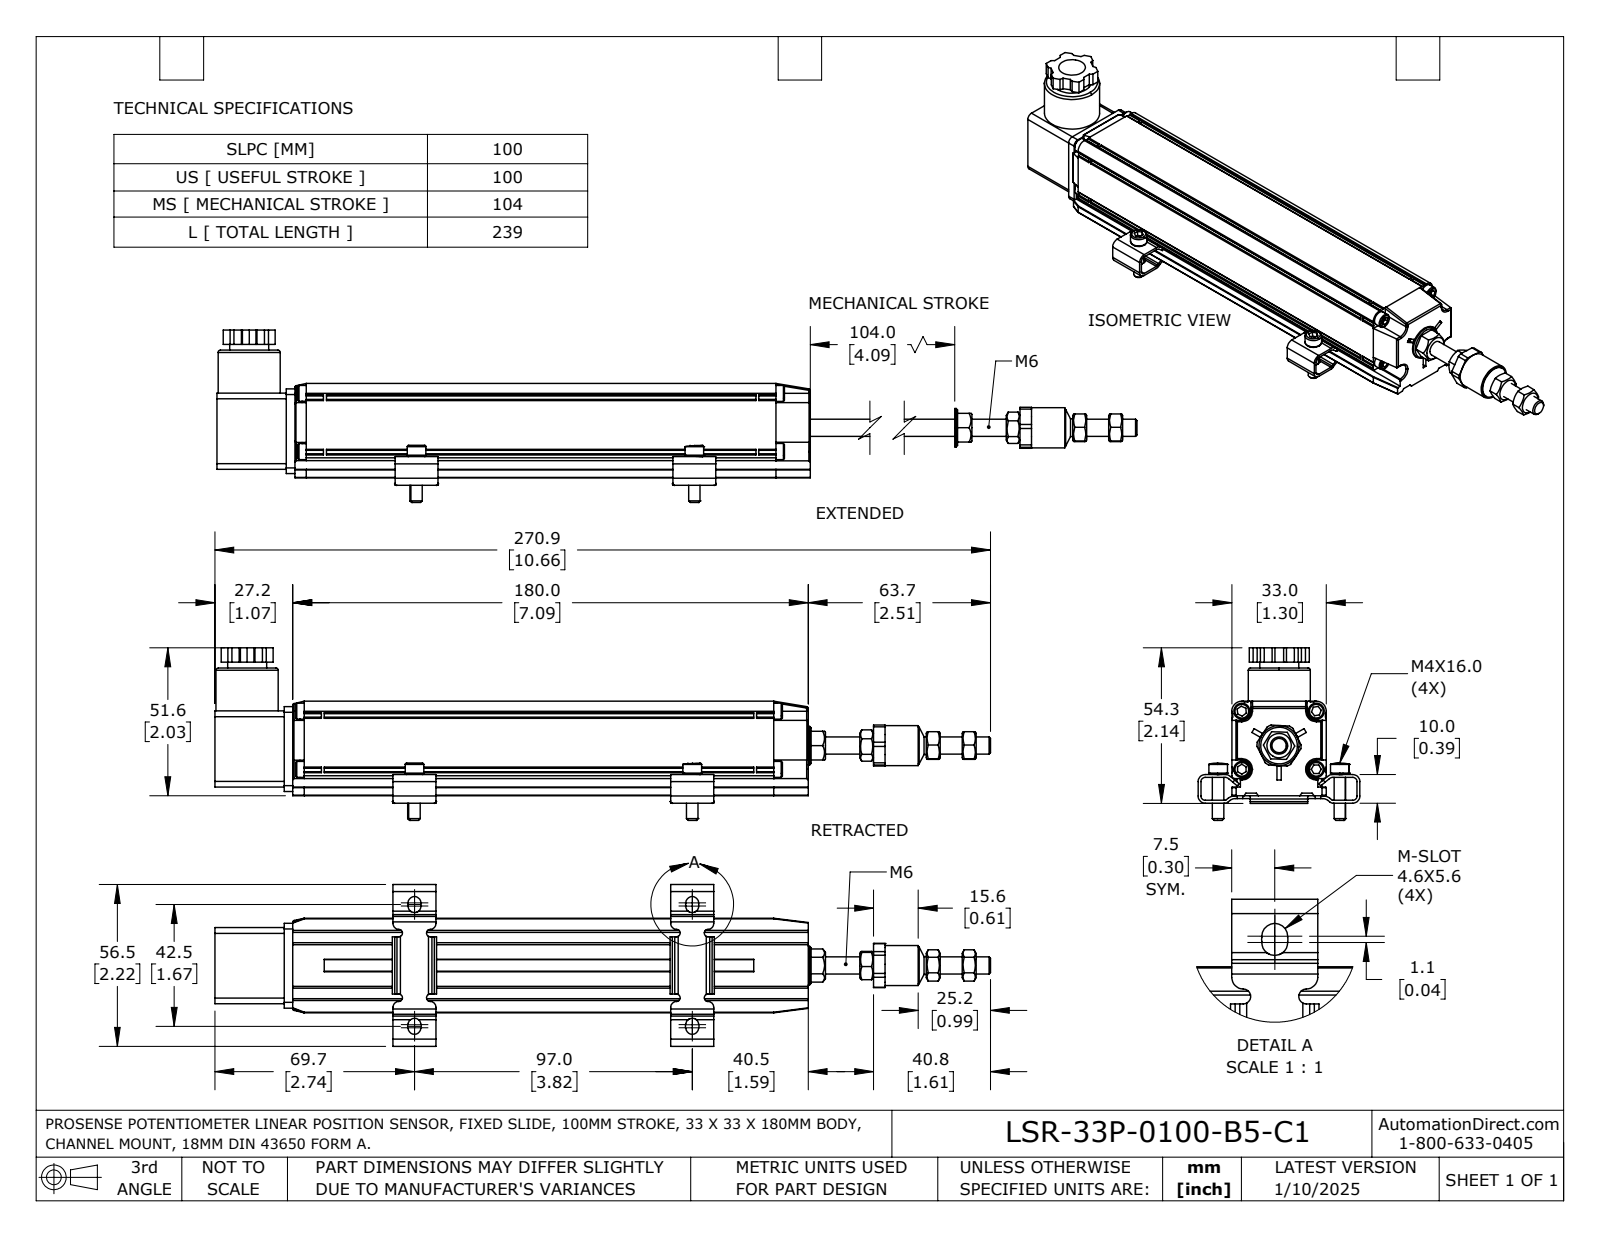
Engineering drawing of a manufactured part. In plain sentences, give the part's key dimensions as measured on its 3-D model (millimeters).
The part is named "LSR-33P-0100-B5-C1". Its 3-D file was written by "SolidWorks 2023 (AUTOMOTIVE_DESIGN)". It is 14 solids with 901 faces: 579 planar, 253 cylindrical and 69 other. Overall it measures 270.8 by 60.2 by 56.5 millimeters. Its volume is 196 600 cubic millimeters and its surface area 63 670 square millimeters. Round holes: 4 of diameter 2.7, 4 of diameter 3.3, 1 of diameter 4.3, 1 of diameter 5.2, 1 of diameter 5.3, 1 of diameter 5.9, 1 of diameter 7, 1 of diameter 7.2, 1 of diameter 10, 1 of diameter 10.5, 1 of diameter 14.6, 1 of diameter 15.3. Round bosses or shafts: 5 of diameter 4, 5 of diameter 3, 4 of diameter 6.5, 4 of diameter 5.6, 1 of diameter 21.7, 1 of diameter 14, 1 of diameter 13.6, 1 of diameter 13.4. Partial cylindrical surfaces (rounded edges, fillets, slot ends): 28 of radius 2, 23 of radius 0.5, 16 of radius 0.2, 8 of radius 1.3, 8 of radius 1.5, 8 of radius 2.3, 8 of radius 3, 4 of radius 1. The main face-to-face distances are 33, 3, 1, 5.6, 30, 1.6, 2.6, 2, 27.4, 25. The hole center spacings are 1.2, 14.8, 15.4, 17.7, 18.5, 20.3, 26, 33.
